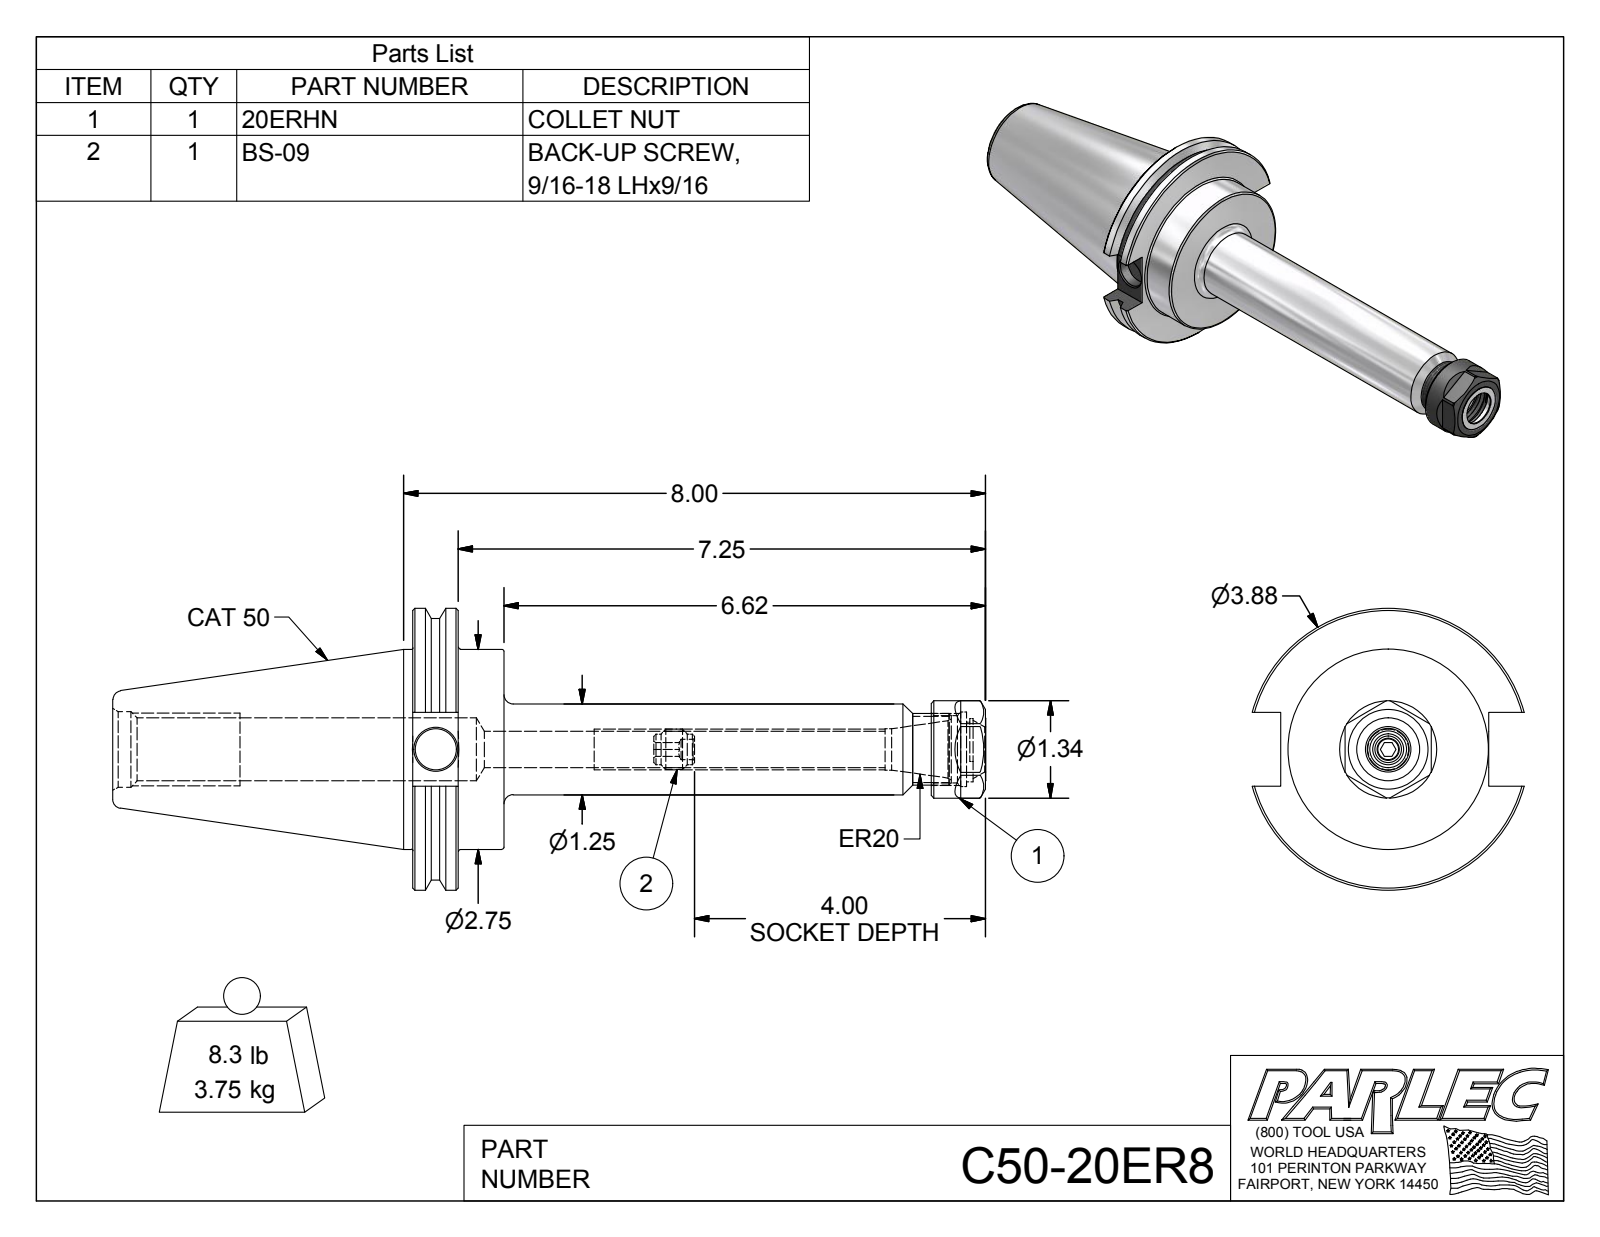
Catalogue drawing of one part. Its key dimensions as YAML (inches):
part_name: "C50-20ER8; C50-20ER8-1; 20ERHN; BS-09"
step_written_by: "Autodesk Inventor 2012 (AUTOMOTIVE_DESIGN)"
units: inches
bodies: {solids: 3, faces: 110, planar: 44, cylindrical: 26, other: 40}
overall_size: [12.005, 3.875, 3.74]
volume: 29.38
surface_area: 116.5
round_holes:
  - {diameter: 0.281, count: 1}
  - {diameter: 0.502, count: 1}
  - {diameter: 0.563, count: 1}
  - {diameter: 0.57, count: 1}
  - {diameter: 0.62, count: 1}
  - {diameter: 0.82, count: 1}
  - {diameter: 0.865, count: 1}
  - {diameter: 0.925, count: 1}
  - {diameter: 1.024, count: 1}
  - {diameter: 1.038, count: 1}
round_bosses_or_shafts:
  - {diameter: 3.875, count: 1}
  - {diameter: 3.594, count: 1}
  - {diameter: 2.75, count: 1}
  - {diameter: 1.339, count: 1}
  - {diameter: 1.25, count: 1}
  - {diameter: 0.984, count: 1}
  - {diameter: 0.86, count: 1}
  - {diameter: 0.555, count: 1}
partial_cylinders:
  - {radius: 0.423, count: 1}
face_to_face_distances: [0.625, 1.255, 0.63, 1.181, 4.125, 4.75, 5.38, 1.015, 11.252, 7.127]
hole_center_spacings: [0.037]
